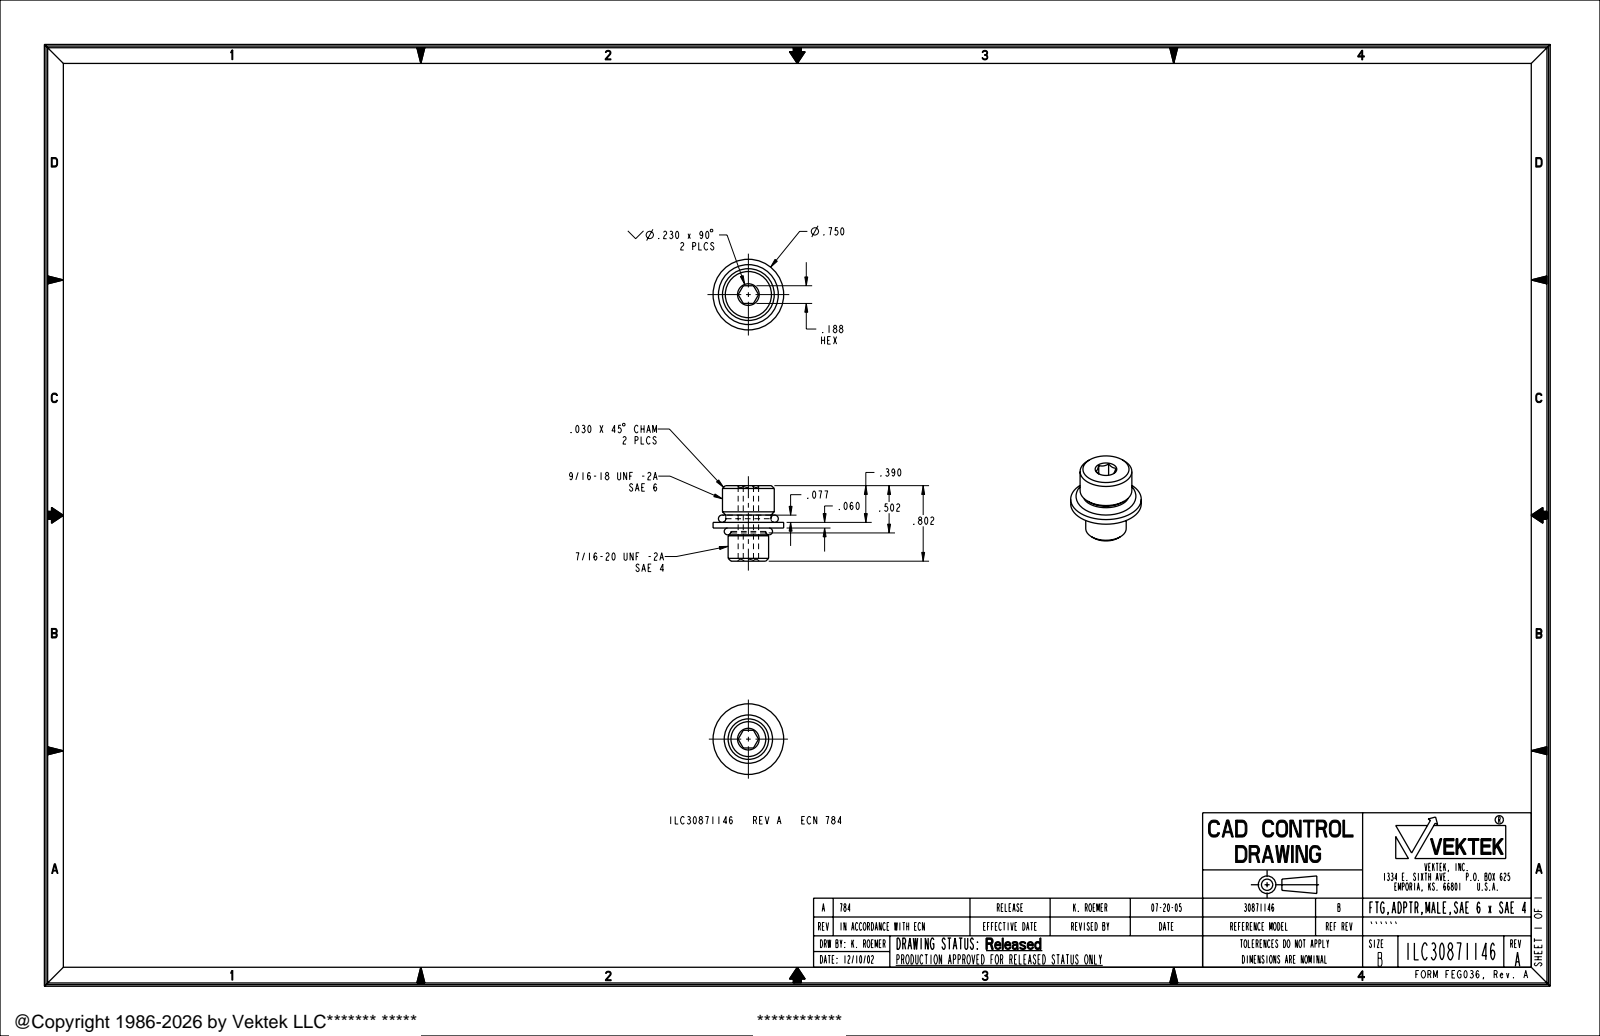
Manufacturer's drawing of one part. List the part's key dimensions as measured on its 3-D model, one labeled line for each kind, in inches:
Part name (STEP PRODUCT): ILC30871146
STEP written by: PRO/ENGINEER BY PARAMETRIC TECHNOLOGY CORPORATION, 2004290 (AUTOMOTIVE_DESIGN_CC2)
Units: inches
Bodies: 1 solid, 41 faces (10 planar, 11 cylindrical, 20 other)
Overall size (bounding box): 0.802 × 0.75 × 0.75
Volume: 0.151 in³ · Surface area: 3.23 in²
Round bosses / shafts (diameter × count): ⌀0.75 ×1, ⌀0.55 ×1, ⌀0.48 ×1, ⌀0.43 ×1, ⌀0.369 ×1
Main face-to-face distances: 0.188, 0.06, 0.45, 0.39, 0.352, 0.412, 0.802
